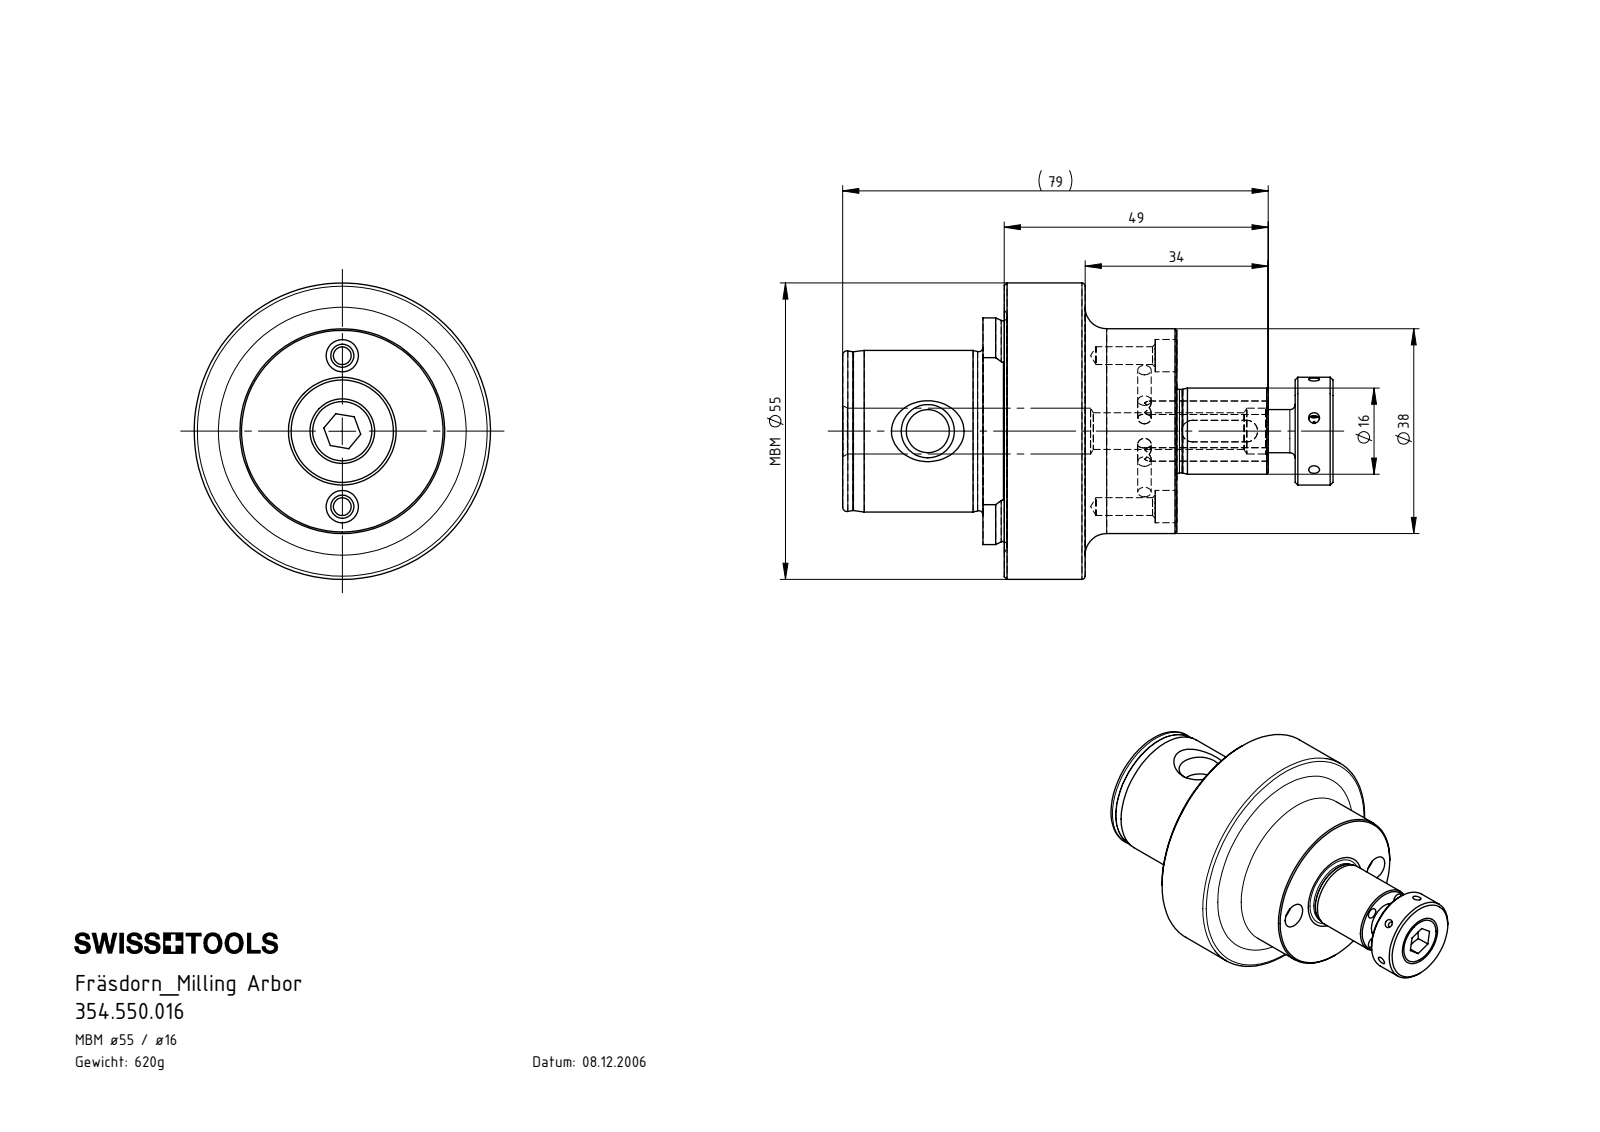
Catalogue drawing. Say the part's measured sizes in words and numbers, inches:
The part is named "MB5-D16.K01.032_D; D16-ER2.002.008_A; D16-ER3.001.014_A; ISO 4762 - M3 x 8 (+4 more)". Its 3-D file was written by "SolidWorks 2017 (CONFIG_CONTROL_DESIGN)". It is 8 solids with 344 faces: 77 planar, 125 cylindrical and 142 other. Overall it measures 3.583 by 2.165 by 2.165 inches. Its volume is 4.941 cubic inches and its surface area 31.36 square inches. Round holes: 11 of diameter 0.079, 4 of diameter 0.098, 1 of diameter 0.138, 1 of diameter 0.236, 1 of diameter 0.268, 1 of diameter 0.315, 1 of diameter 0.335, 1 of diameter 0.433. Round bosses or shafts: 1 of diameter 2.165, 1 of diameter 1.535, 1 of diameter 1.181, 1 of diameter 0.787, 1 of diameter 0.63, 1 of diameter 0.61, 1 of diameter 0.472, 1 of diameter 0.315. Partial cylindrical surfaces (rounded edges, fillets, slot ends): 4 of radius 0.079, 1 of radius 0.157, 1 of radius 0.828. The main face-to-face distances are 1.26, 0.669, 1.181, 2.441, 1.772, 0.591, 1.026, 0.156, 0.746, 1.415. The hole center spacings are 0.295, 0.511, 0.295, 0.59, 0.147, 0.15, 0.241, 0.38.
